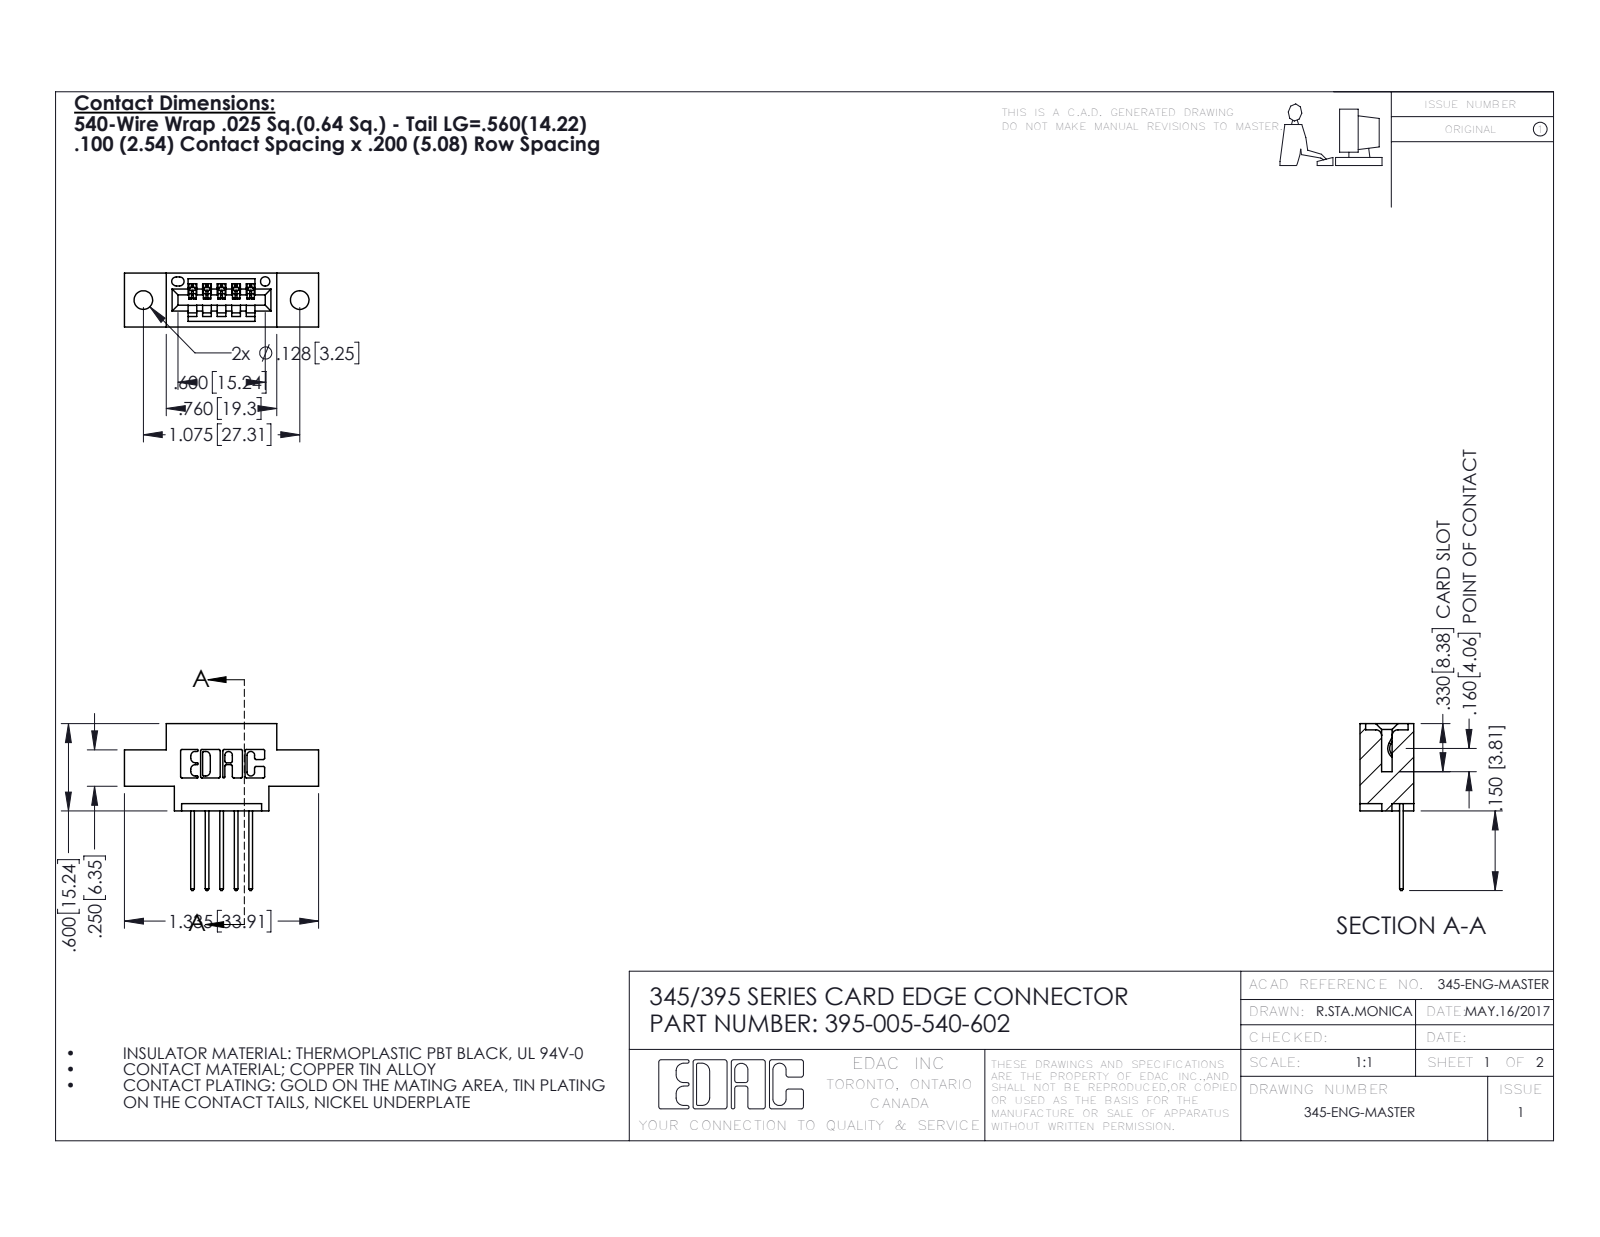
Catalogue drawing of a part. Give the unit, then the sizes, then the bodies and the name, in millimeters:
Units: millimetres
Overall size (bounding box): 33.9 × 29.1 × 9.4
Round holes (diameter × count): ⌀3.3 ×2, ⌀1.6 ×1
Partial cylindrical surfaces — rounded edges, fillets, slot ends (radius × count): R0.3 ×22, R0.2 ×10, R0.3 ×10, R0.2 ×6, R0.8 ×6, R0.7 ×3, R0.8 ×2, R1 ×2
Main face-to-face distances: 9.4, 5.1, 7.6, 1.8, 2.5, 0.6, 2.5, 6.9, 6.4, 1.5
Hole centre spacings: 6.9, 21.5, 27.3
Volume: 2 770 mm³ · Surface area: 3 088 mm²
Bodies: 6 solids, 420 faces (284 planar, 136 cylindrical, 0 other)
Part name (STEP PRODUCT): 345-292-001_345-293-140; 395-005-540-602; 345 Part_0.170 Offset - 0.128 Dia
STEP written by: SolidWorks 2016 (CONFIG_CONTROL_DESIGN)
